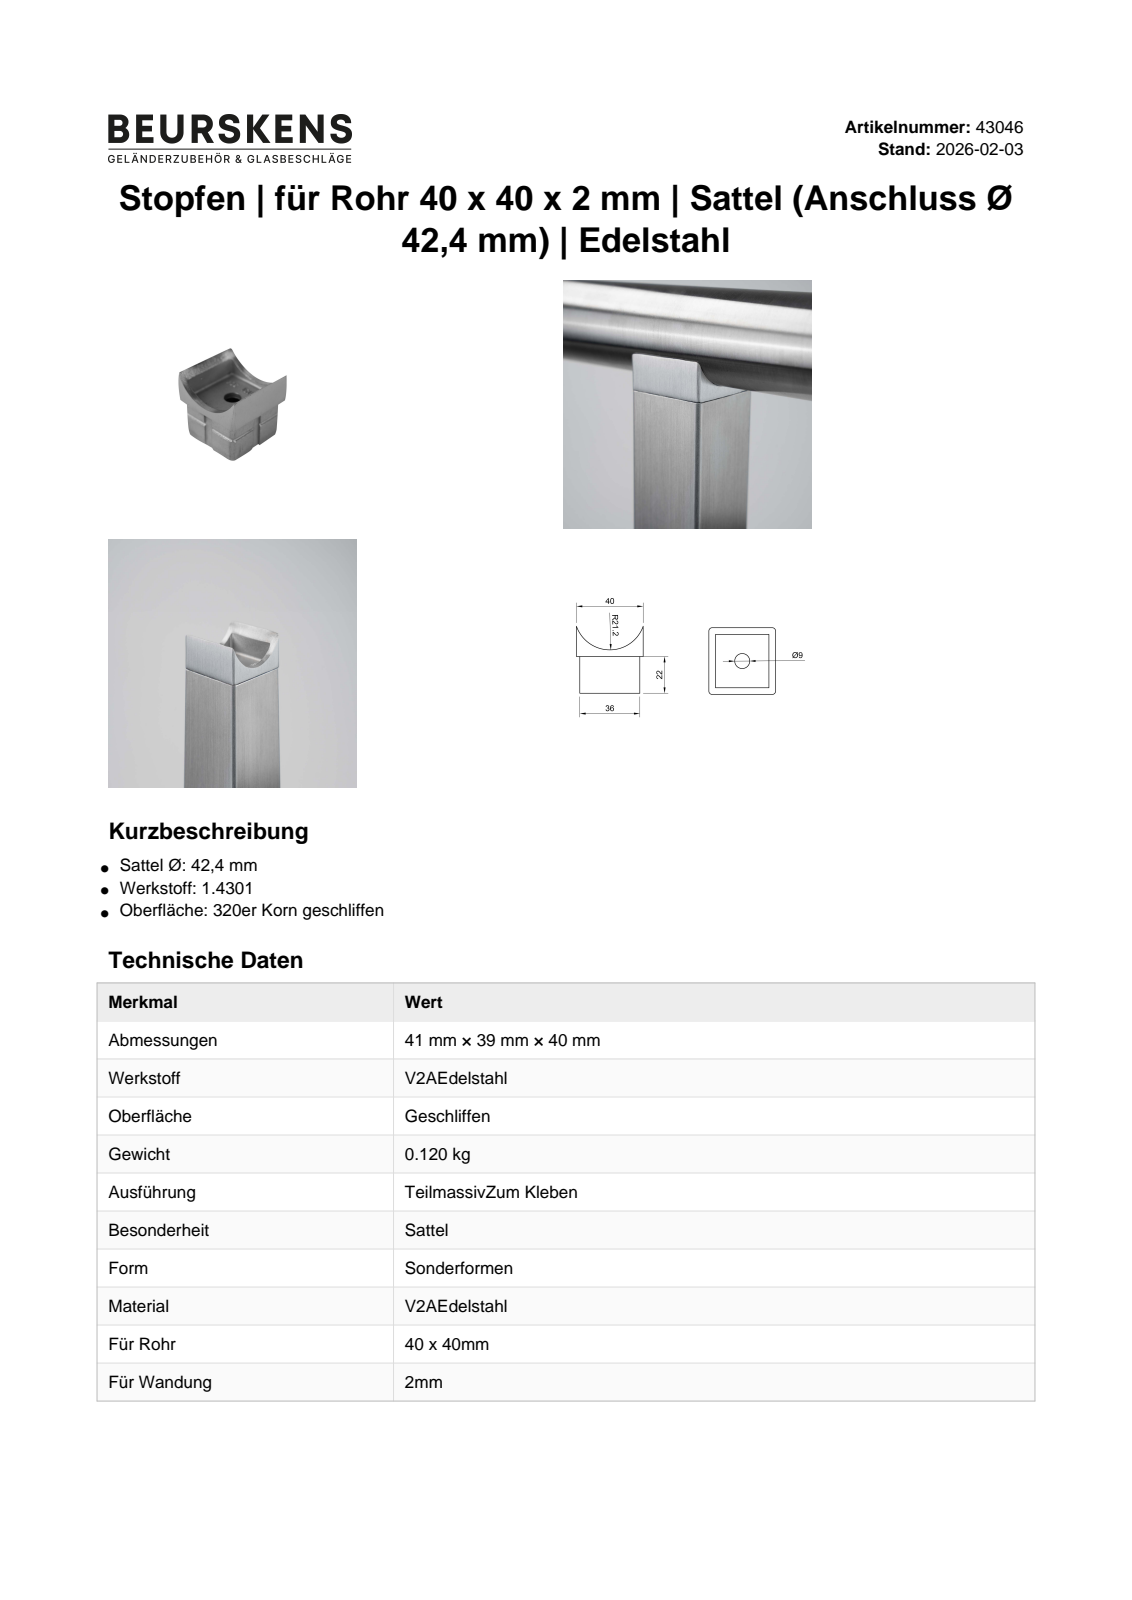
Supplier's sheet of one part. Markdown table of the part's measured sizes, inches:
| quantity | value |
| --- | --- |
| part name | 43046 |
| STEP written by | Autodesk Inventor 2022 (AUTOMOTIVE_DESIGN) |
| units | inches |
| bodies | 1 solid, 30 faces (20 planar, 10 cylindrical, 0 other) |
| overall size | 1.581 × 1.575 × 1.575 |
| volume | 0.849 in³ |
| surface area | 19 in² |
| round holes (diameter × count) | 0.354 × 1 |
| partial cylindrical surfaces (radius × count) | 0.079 × 8, 0.835 × 1 |
| main face-to-face distances | 0.079, 1.417, 1.339, 1.26, 0.157, 1.496, 1.575, 0.055, 0.134, 0.866 |
